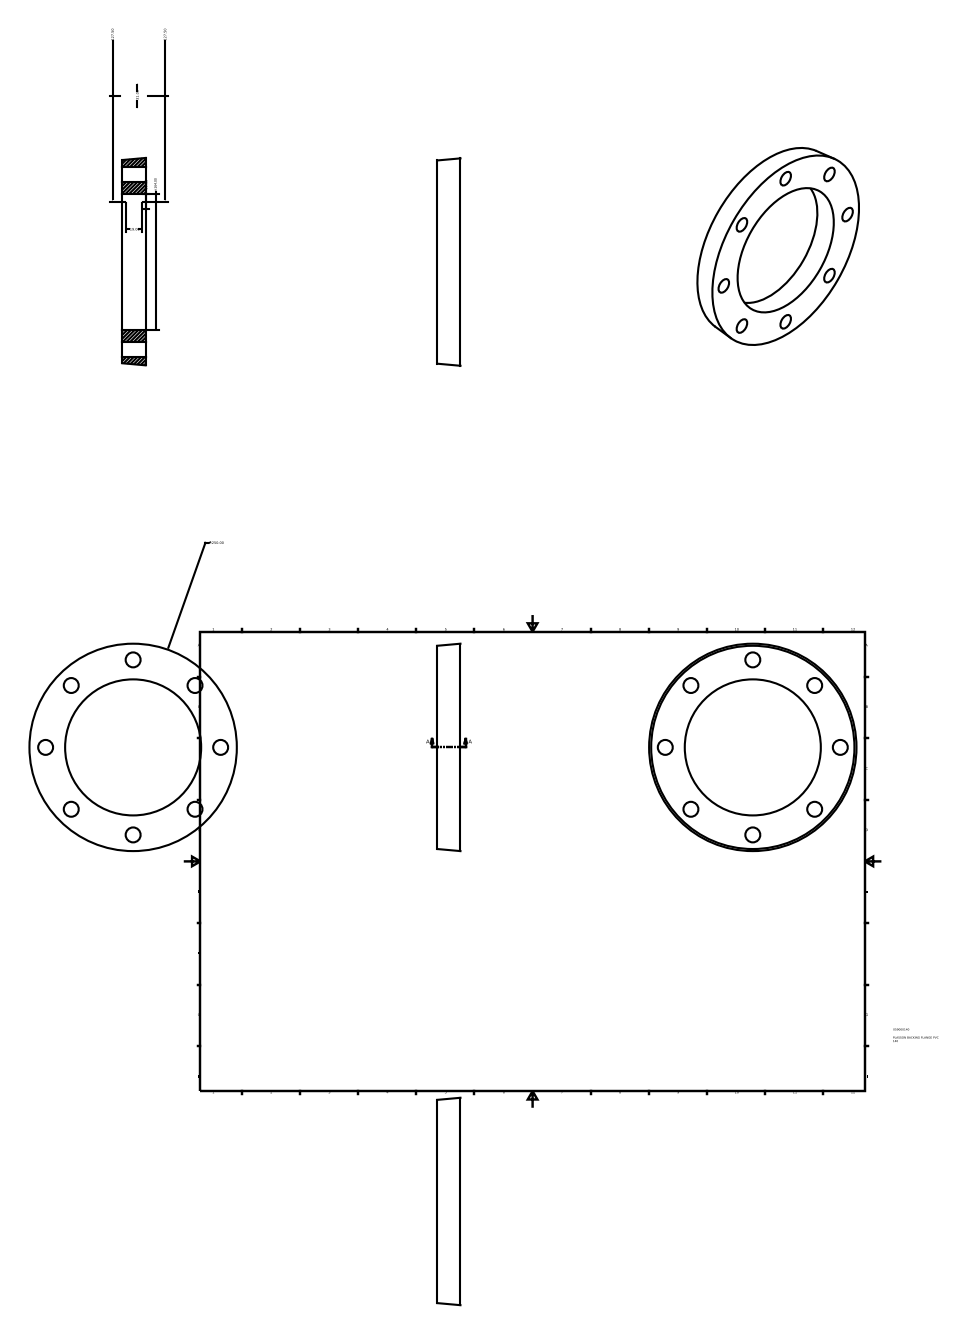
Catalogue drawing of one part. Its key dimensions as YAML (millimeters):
part_name: "059000140"
step_written_by: "Autodesk Inventor 2015 (AUTOMOTIVE_DESIGN)"
units: millimeters
bodies: {solids: 1, faces: 12, planar: 2, cylindrical: 9, other: 1}
overall_size: [250, 250, 28]
volume: 698666
surface_area: 98862
round_holes:
  - {diameter: 18, count: 8}
  - {diameter: 164, count: 1}
face_to_face_distances: [28]
hole_center_spacings: [80.75, 105.5, 149.2, 194.94, 211]
